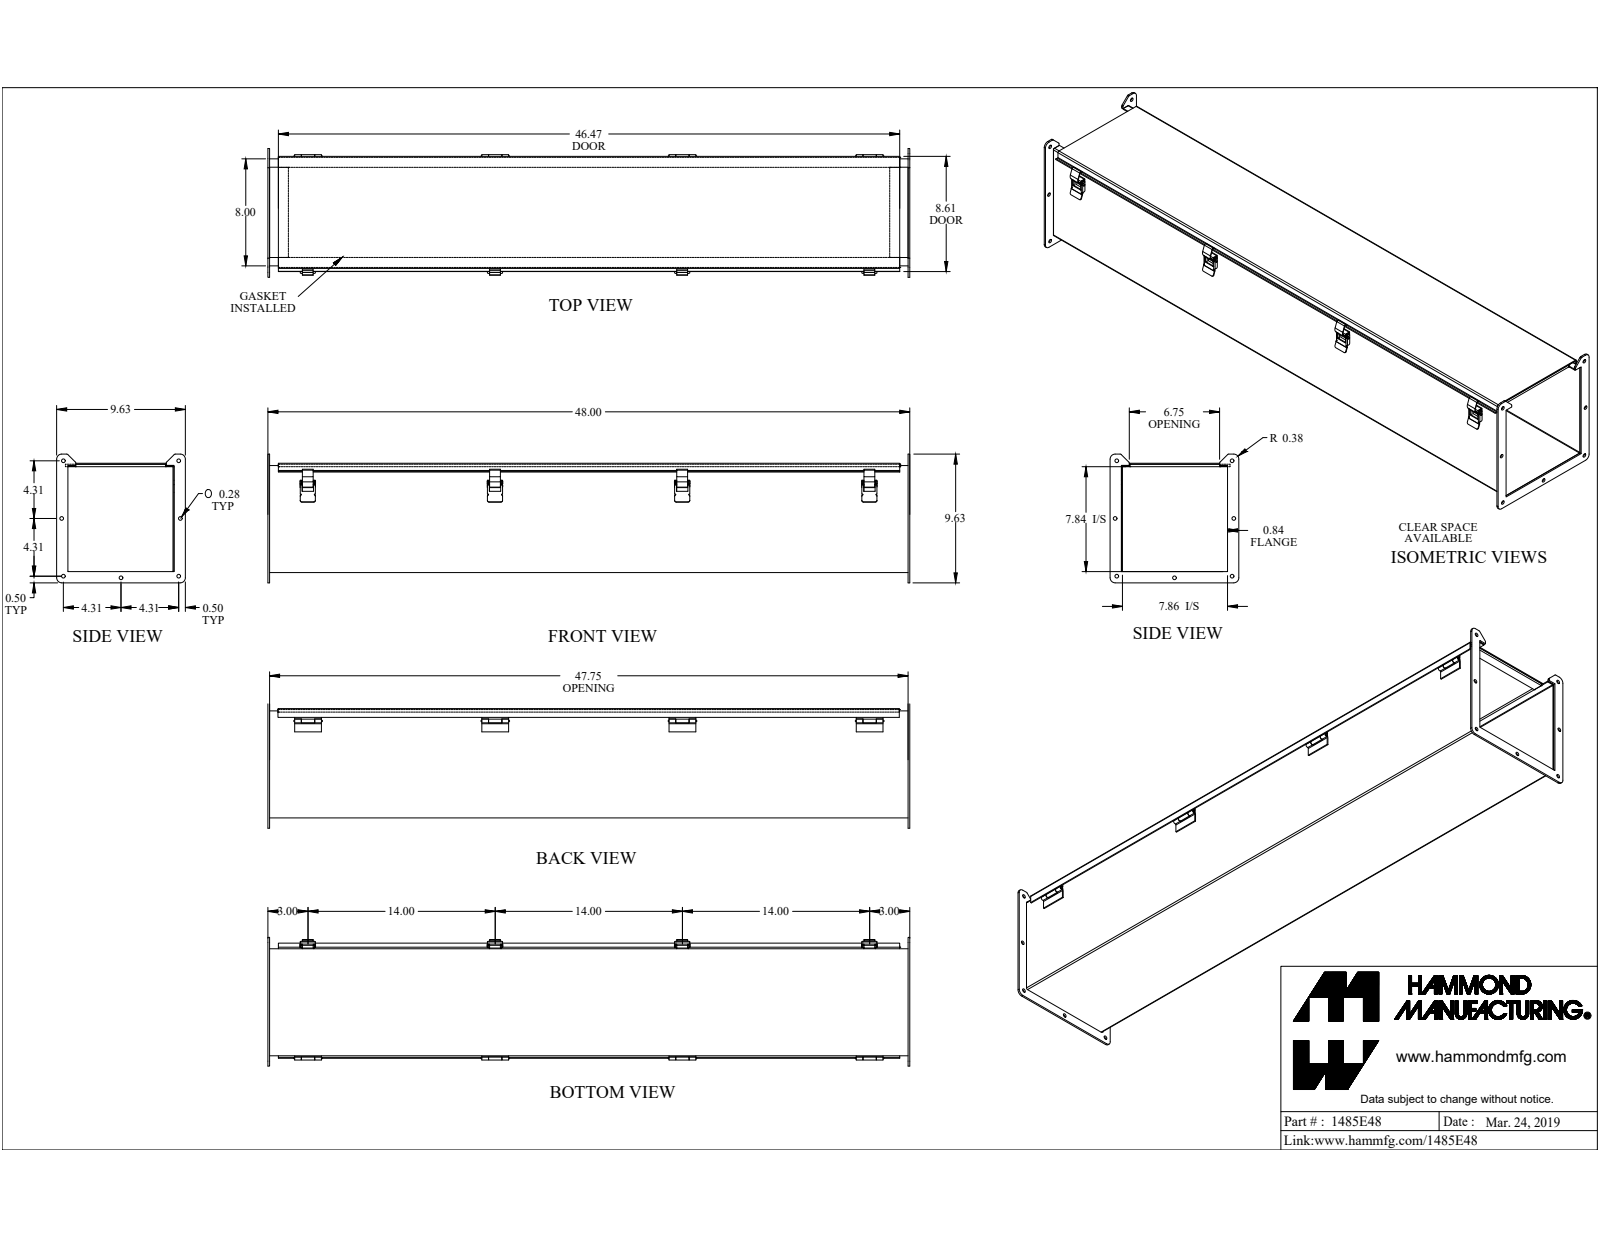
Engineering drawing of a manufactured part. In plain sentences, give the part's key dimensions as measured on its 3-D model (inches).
The part is named "1485E48". Its 3-D file was written by "SolidWorks 2019 (CONFIG_CONTROL_DESIGN)". It is 32 solids with 706 faces: 418 planar, 280 cylindrical and 8 other. Overall it measures 48 by 9.625 by 9.625 inches. Its volume is 140.7 cubic inches and its surface area 3 679 square inches. Round holes: 7 of diameter 0.281, 1 of diameter 0.125, 1 of diameter 0.13, 1 of diameter 0.164. Round bosses or shafts: 2 of diameter 0.187, 1 of diameter 0.275, 1 of diameter 0.156, 1 of diameter 0.125, 1 of diameter 0.125. Partial cylindrical surfaces (rounded edges, fillets, slot ends): 25 of radius 0.016, 13 of radius 0.125, 9 of radius 0.035, 9 of radius 0.039, 9 of radius 0.076, 8 of radius 0.015, 8 of radius 0.029, 8 of radius 0.086. The main face-to-face distances are 0.072, 7.928, 8.1, 8, 7.856, 8.028, 8.172, 0.172, 7.913, 7.841. The hole center spacings are 8.625, 4.314, 4.315, 9.755, 9.755, 6.276, 12.197, 0.285.
